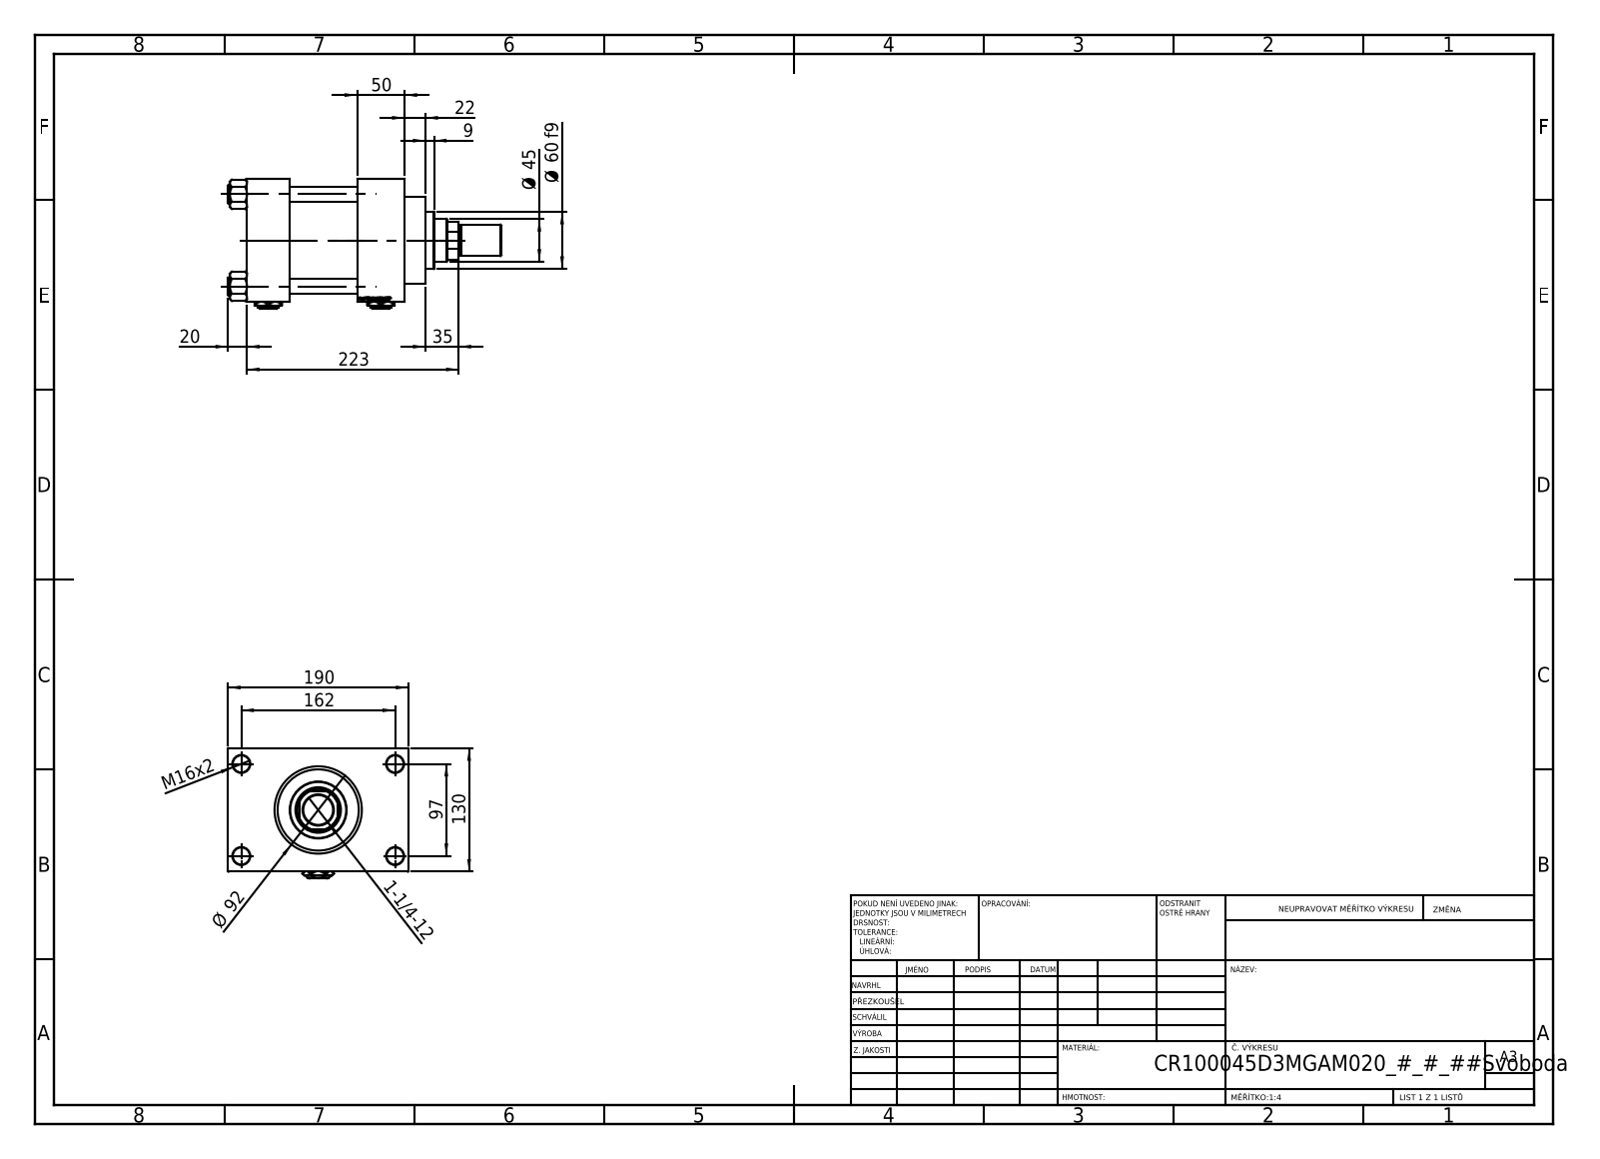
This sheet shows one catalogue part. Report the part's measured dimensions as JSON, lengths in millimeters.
{"part_name": "ROD_END_AH; V215CR_D_TYCINKA; Zatka_pro_OIL_PORT; V215CR_VCP_D (+3 more)", "step_written_by": "SolidWorks 2019 (CONFIG_CONTROL_DESIGN)", "units": "millimeters", "bodies": {"solids": 14, "faces": 1267, "planar": 597, "cylindrical": 104, "other": 566}, "overall_size": [288, 190, 137], "volume_mm3": 2631000, "surface_area_mm2": 365776, "round_holes": [[16, 4], [18, 4], [7, 2], [26.44, 2], [35, 2], [31.5, 1], [45, 1], [48, 1], [76, 1], [85.5, 1], [100, 1]], "round_bosses_or_shafts": [[19, 4], [106, 1], [92, 1], [60, 1], [33, 1], [31, 1]], "partial_cylinders_radius": [[22, 1]], "face_to_face_distances": [45, 130, 116, 71, 166, 121, 50, 160, 30, 20], "hole_center_spacings": [32.55, 68.52, 94.41, 96.9, 102.27, 129.45, 161.73, 97]}
